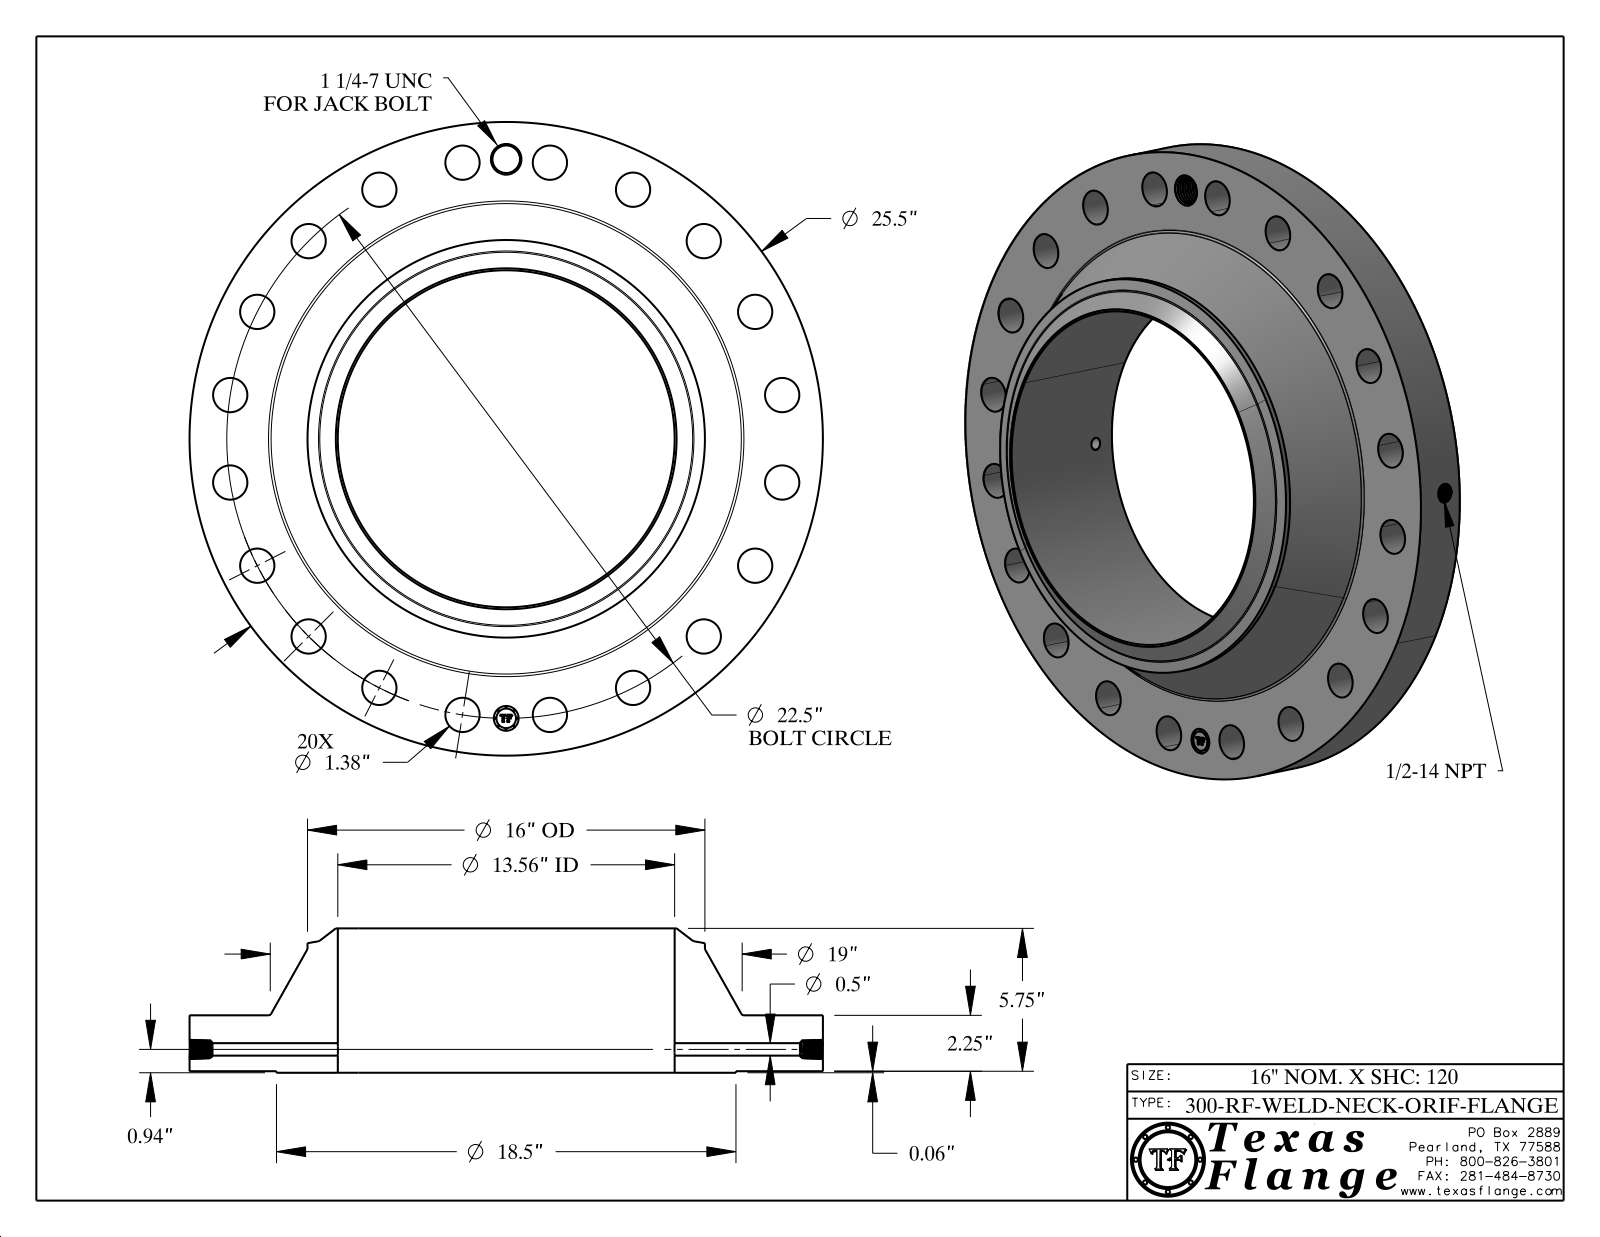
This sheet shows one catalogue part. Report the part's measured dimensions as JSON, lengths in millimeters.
{"part_name": "300-RF-WELD-NECK", "step_written_by": "CATIA V5 STEP AP214 (AUTOMOTIVE_DESIGN)", "units": "millimeters", "bodies": {"solids": 1, "faces": 803, "planar": 369, "cylindrical": 119, "other": 315}, "overall_size": [647.7, 647.7, 147.6], "volume_mm3": 17090000, "surface_area_mm2": 926400, "round_holes": [[35.1, 20], [12.7, 1], [17.1, 1], [25.4, 1], [28.2, 1], [344.5, 1]], "round_bosses_or_shafts": [[1.5, 8], [647.7, 1], [469.9, 1], [406.4, 1], [20, 1]], "face_to_face_distances": [57.2, 1.5, 58.7, 147.6, 146.1, 88.9, 58.3, 56.8, 0.4, 89.3], "hole_center_spacings": [89.4, 259.5, 462.4, 509.2, 543.5, 176.6, 285.8, 335.9]}
